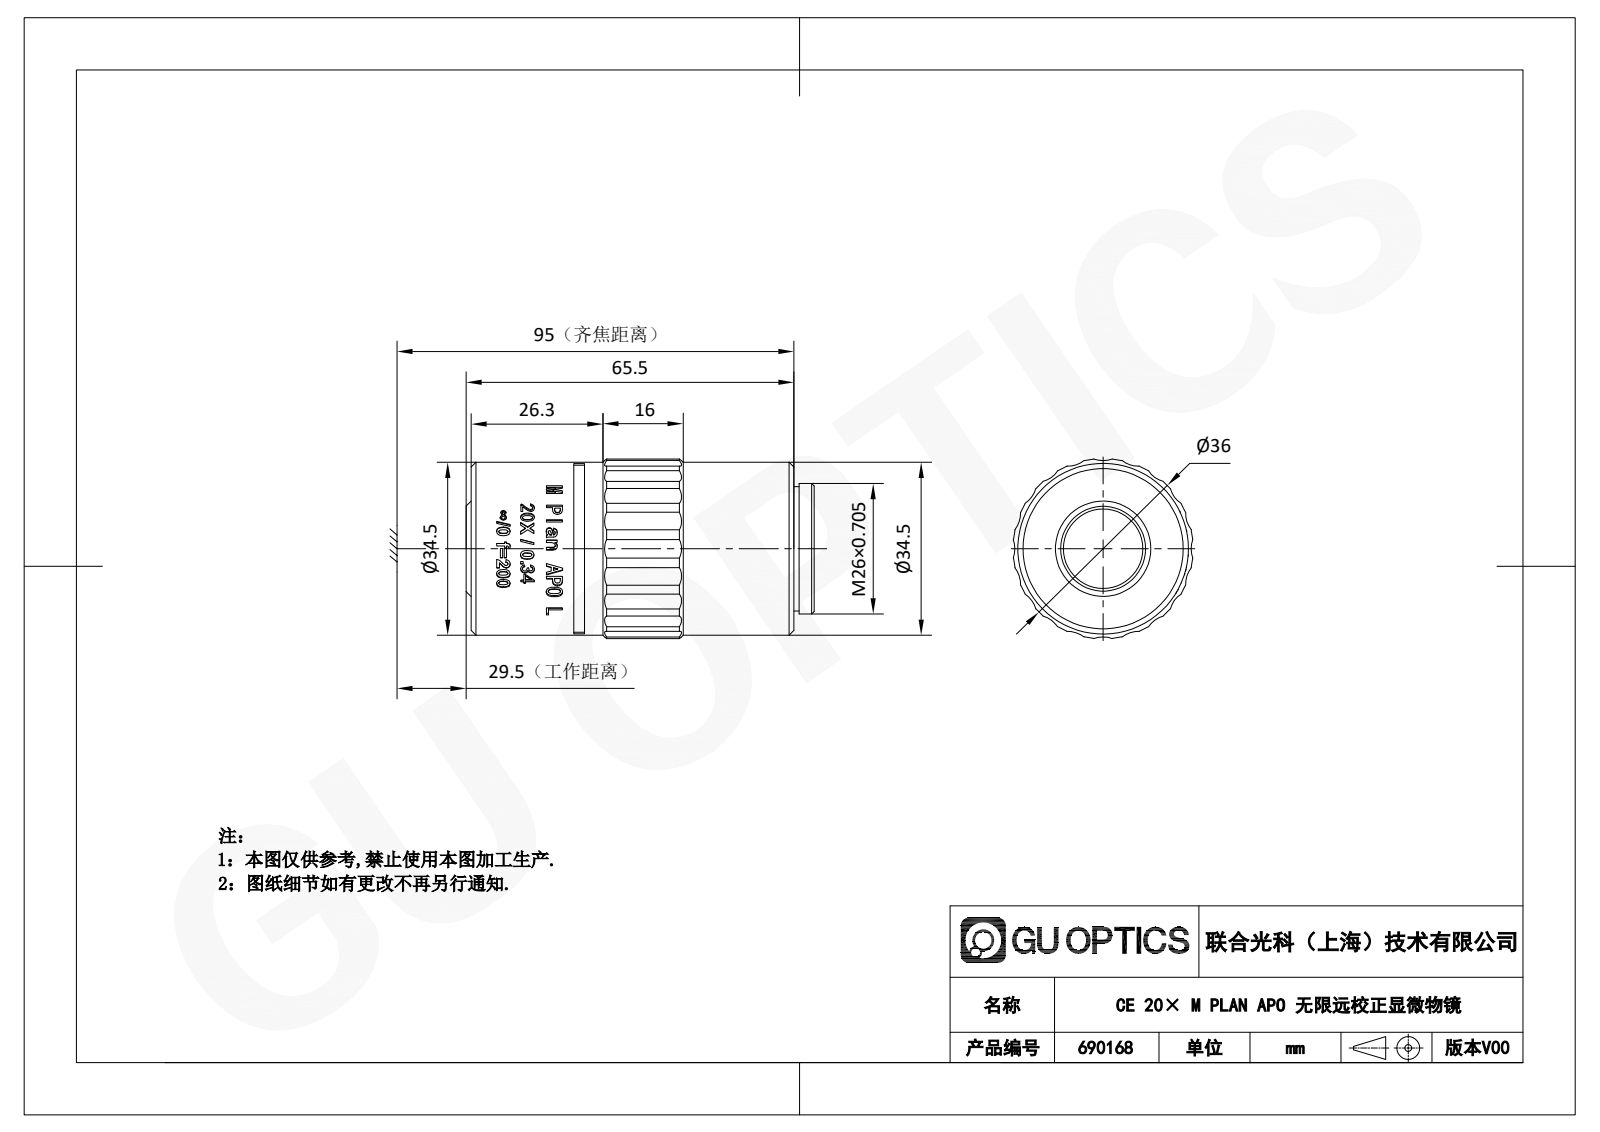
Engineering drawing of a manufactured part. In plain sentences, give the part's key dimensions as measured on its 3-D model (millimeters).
The part is named "690166". Its 3-D file was written by "SolidWorks 2020 (CONFIG_CONTROL_DESIGN)". It is 1 solid with 383 faces: 118 planar, 96 cylindrical and 169 other. Overall it measures 69.41 by 35.81 by 35.81 millimeters. Its volume is 62 192 cubic millimeters and its surface area 9 647 square millimeters. Round holes: 1 of diameter 15, 1 of diameter 22. Round bosses or shafts: 1 of diameter 34.5, 1 of diameter 33.88, 1 of diameter 26, 1 of diameter 24.8. Partial cylindrical surfaces (rounded edges, fillets, slot ends): 20 of radius 5.29, 1 of radius 16.84, 1 of radius 17.05, 1 of radius 18. The main face-to-face distances are 65.71, 1.31, 64.4, 0.5, 66.21, 64.9, 2.7, 4.01, 68.41, 68.91.
